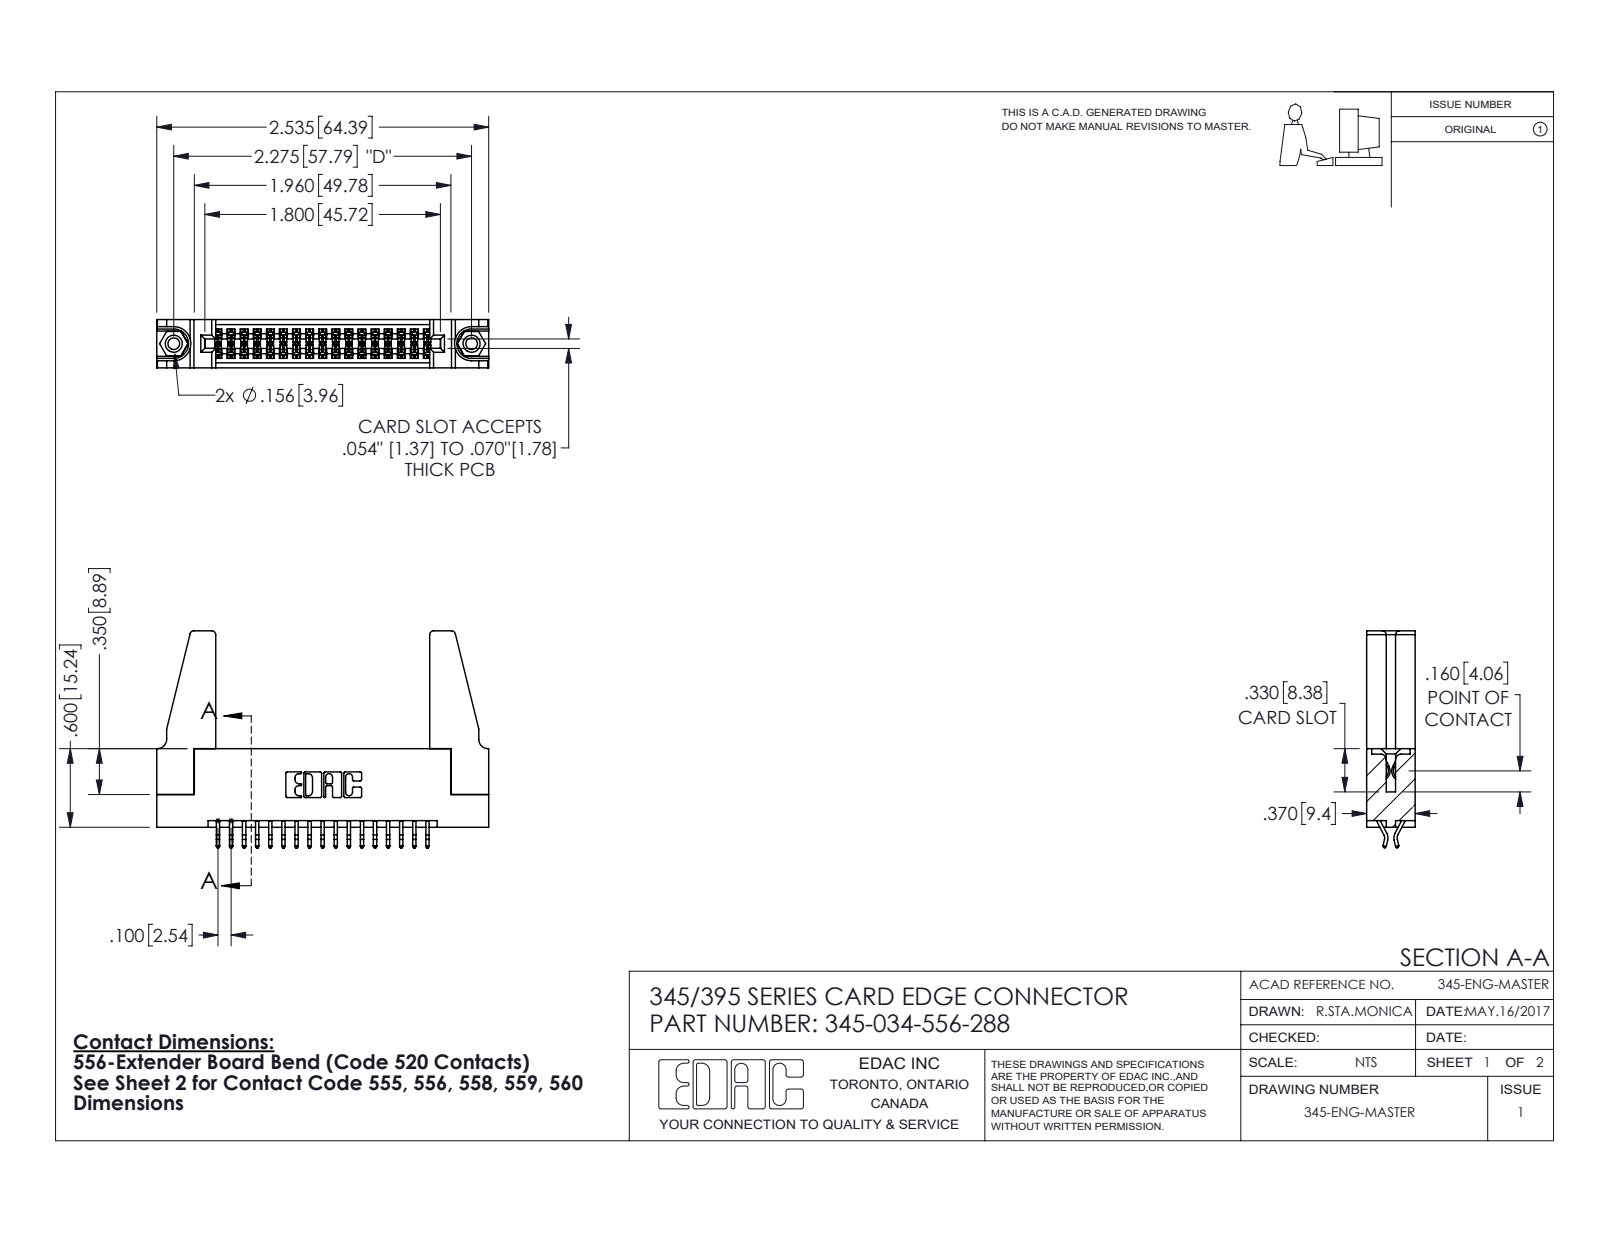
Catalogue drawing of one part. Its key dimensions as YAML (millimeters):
part_name: "345-220-078_345-220-088; 345-250-001_345-250-001-102; 345-292-001_556 Tail; 345 Part_Flush Mounting Lugs - 0.156 Dia-TH (+1 more)"
step_written_by: "SolidWorks 2016 (CONFIG_CONTROL_DESIGN)"
units: millimeters
bodies: {solids: 39, faces: 2154, planar: 1410, cylindrical: 728, other: 16}
overall_size: [64.4, 42.1, 9.4]
volume: 9280
surface_area: 11510
round_holes:
  - {diameter: 2.3, count: 2}
  - {diameter: 3.2, count: 2}
  - {diameter: 4, count: 2}
  - {diameter: 1.6, count: 1}
round_bosses_or_shafts:
  - {diameter: 3.9, count: 2}
partial_cylinders:
  - {radius: 0.2, count: 51}
  - {radius: 0.3, count: 22}
  - {radius: 0.8, count: 8}
  - {radius: 0.2, count: 6}
  - {radius: 0.8, count: 6}
  - {radius: 0.7, count: 3}
  - {radius: 0.3, count: 2}
  - {radius: 0.4, count: 2}
face_to_face_distances: [9.4, 1.8, 7.6, 5.1, 0.6, 2.5, 6.9, 5.7, 3.8, 3.8]
hole_center_spacings: [6.9, 51.8, 57.8]
